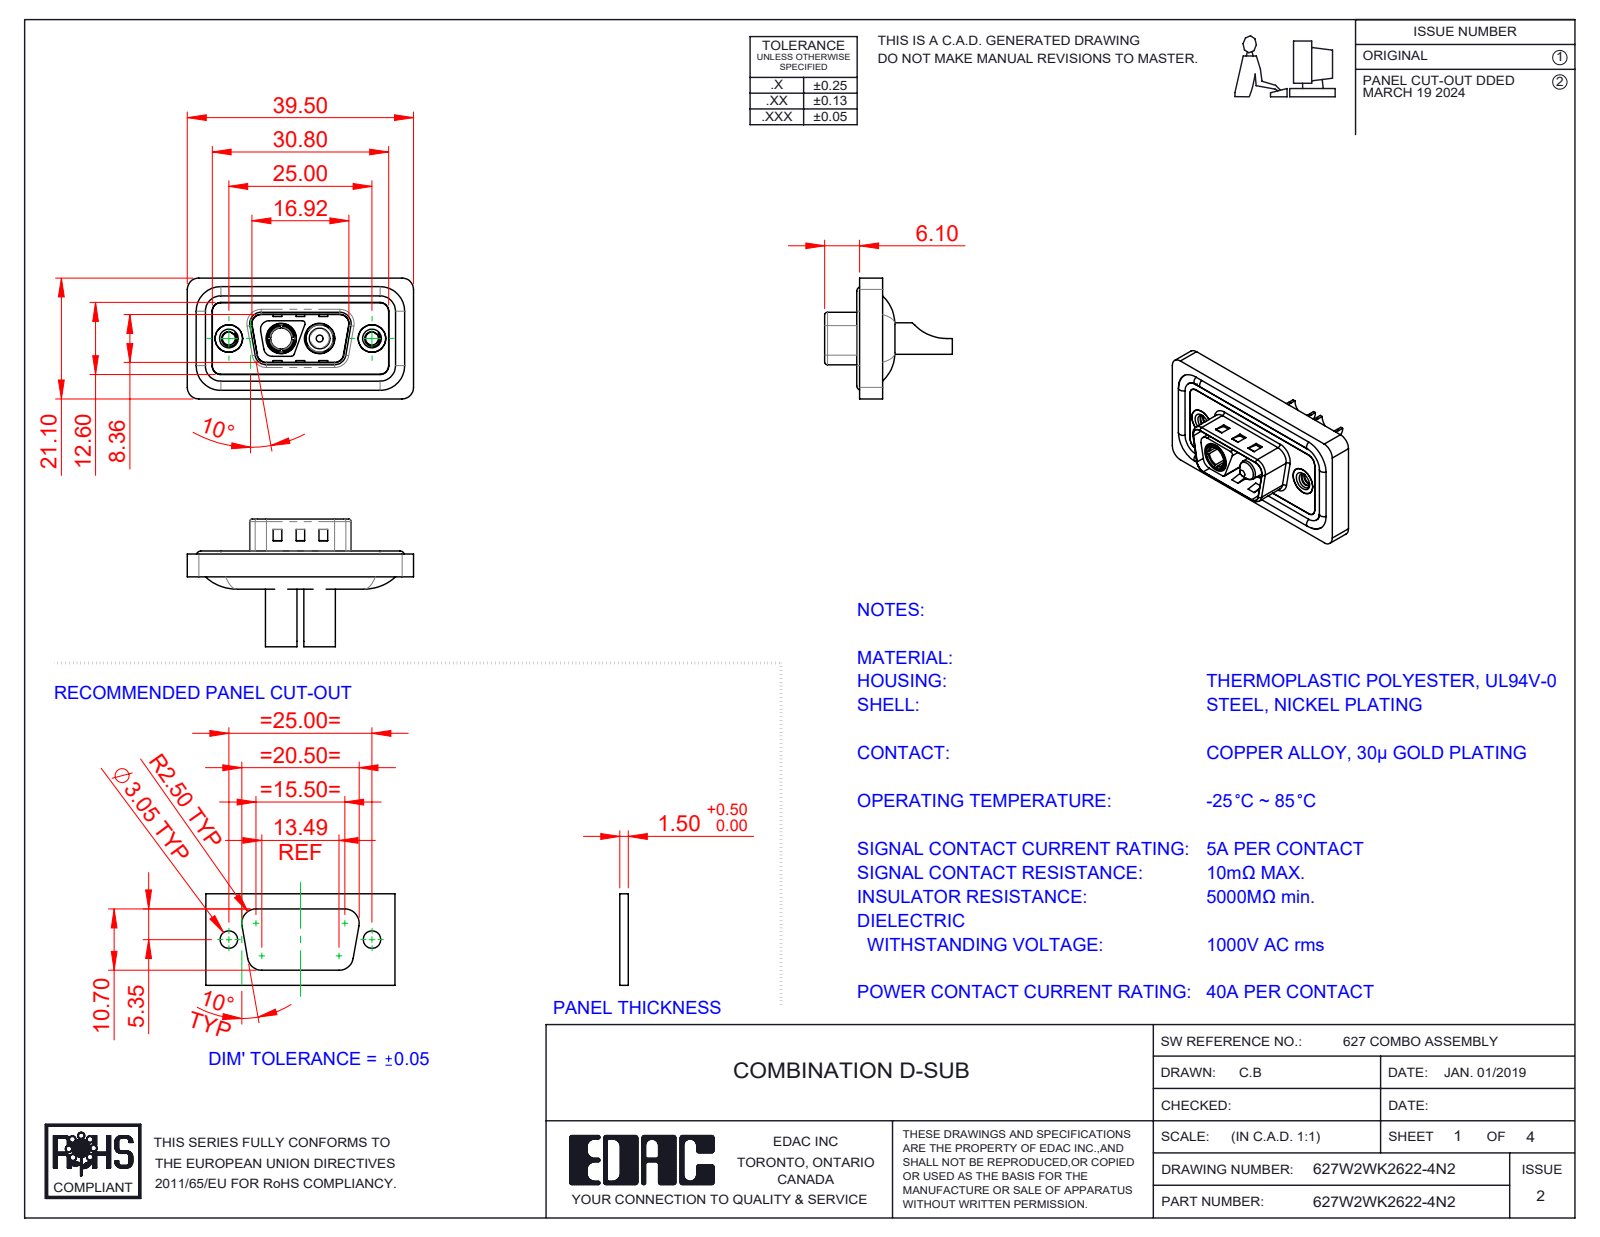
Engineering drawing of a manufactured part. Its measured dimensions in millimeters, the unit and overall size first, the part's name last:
Units: millimetres
Overall size (bounding box): 39.5 × 22.3 × 21.1
Round holes (diameter × count): ⌀2.26 ×2, ⌀4 ×2, ⌀4.6 ×2, ⌀4.8 ×2, ⌀4.85 ×2, ⌀5 ×2, ⌀5.3 ×2, ⌀3.7 ×1
Round bosses / shafts (diameter × count): ⌀1.6 ×4, ⌀5.5 ×2, ⌀5.2 ×2, ⌀4.9 ×2, ⌀4.75 ×2, ⌀3.75 ×2, ⌀4.96 ×1, ⌀3.6 ×1
Partial cylindrical surfaces — rounded edges, fillets, slot ends (radius × count): R1.5 ×24, R2 ×18, R0.5 ×10, R1.6 ×8, R0.25 ×4, R0.6 ×4, R0.65 ×4, R0.9 ×4
Main face-to-face distances: 0.4, 1.1, 2.9, 0.5, 3.1, 1.6, 2.5, 1.8, 3.2, 1.5
Hole centre spacings: 9.14, 15.86, 6.72, 25
Volume: 4 634 mm³ · Surface area: 7 622 mm²
Bodies: 11 solids, 542 faces (193 planar, 229 cylindrical, 120 other)
Part name (STEP PRODUCT): 627Combo Housing_2WK2; Power Socket_40A SC; 627Combo Threaded Rivet_2; 627Combo Waterproof Housing_09 Contacts (+4 more)
STEP written by: SolidWorks 2023 (CONFIG_CONTROL_DESIGN)
